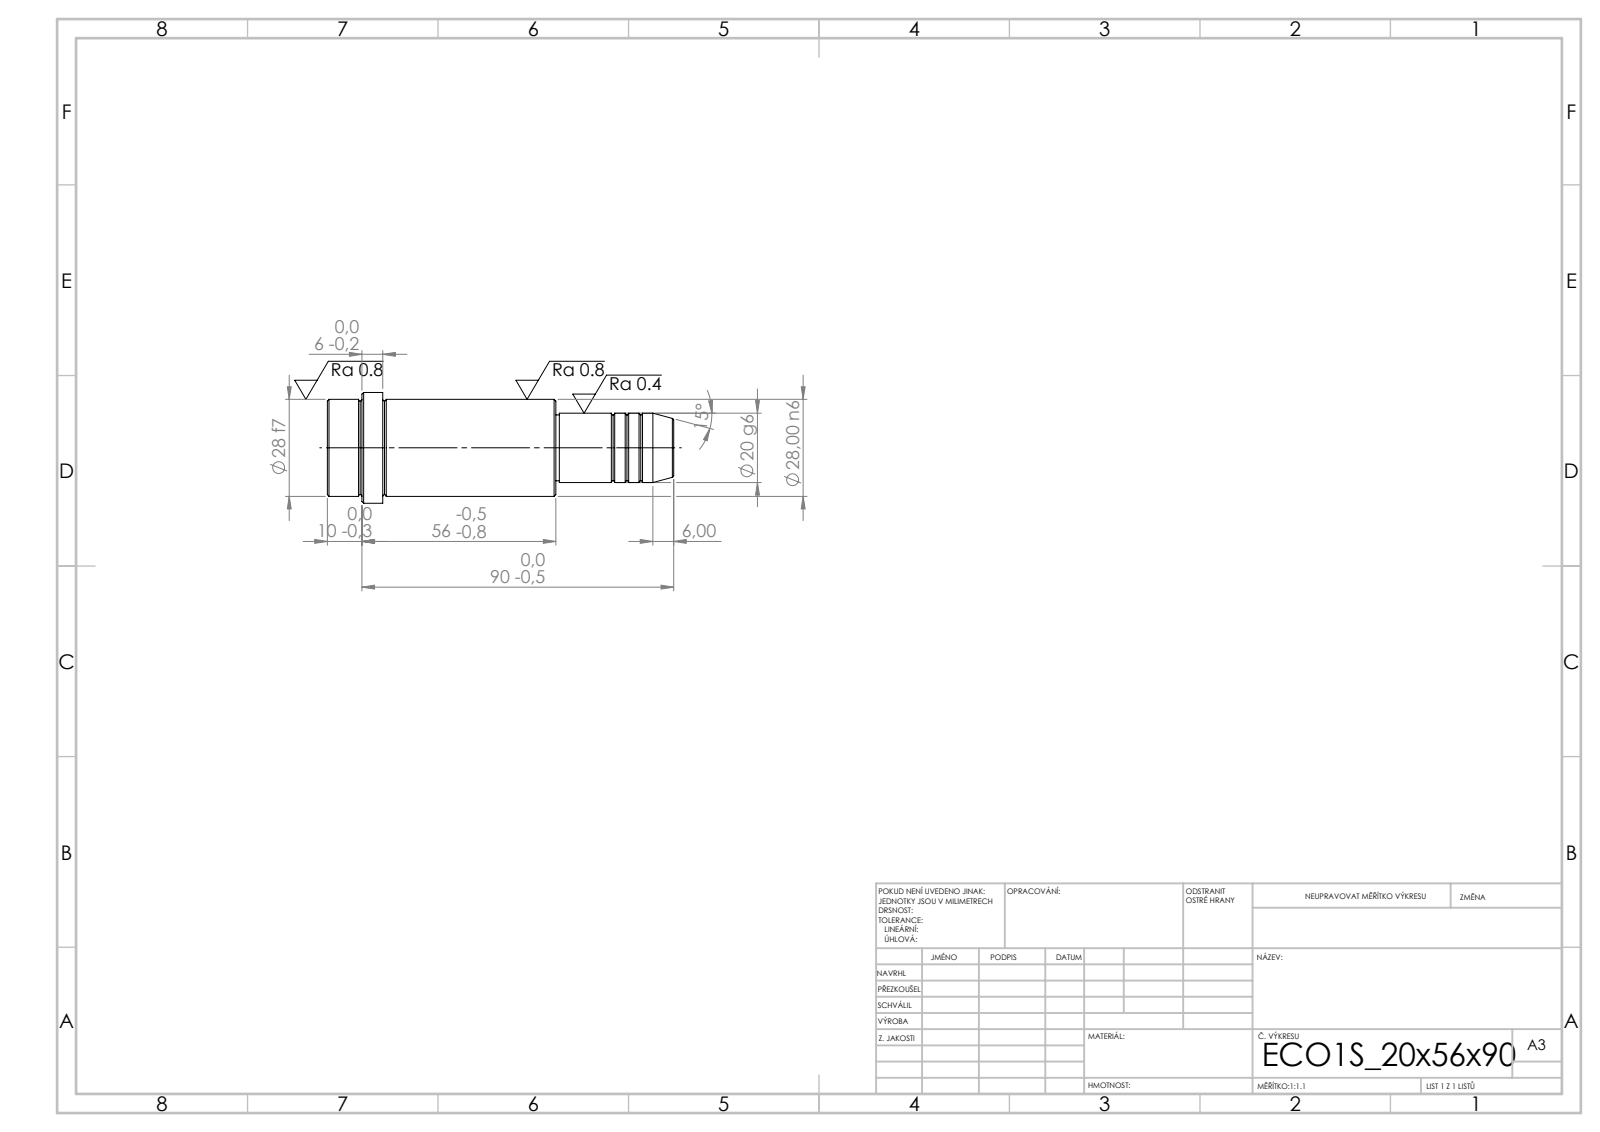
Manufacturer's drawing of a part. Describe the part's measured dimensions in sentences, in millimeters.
Its 3-D file was written by "SolidWorks 2019 (CONFIG_CONTROL_DESIGN)". It is 1 solid with 52 faces: 6 planar, 16 cylindrical and 30 other. Overall it measures 100 by 32 by 32 millimeters. Its volume is 51 958 cubic millimeters and its surface area 9 677 square millimeters. Round bosses or shafts: 1 of diameter 32, 1 of diameter 28, 1 of diameter 20, 1 of diameter 19. The main face-to-face distances are 66, 34, 100, 84, 50, 16, 90, 56, 6, 10.
